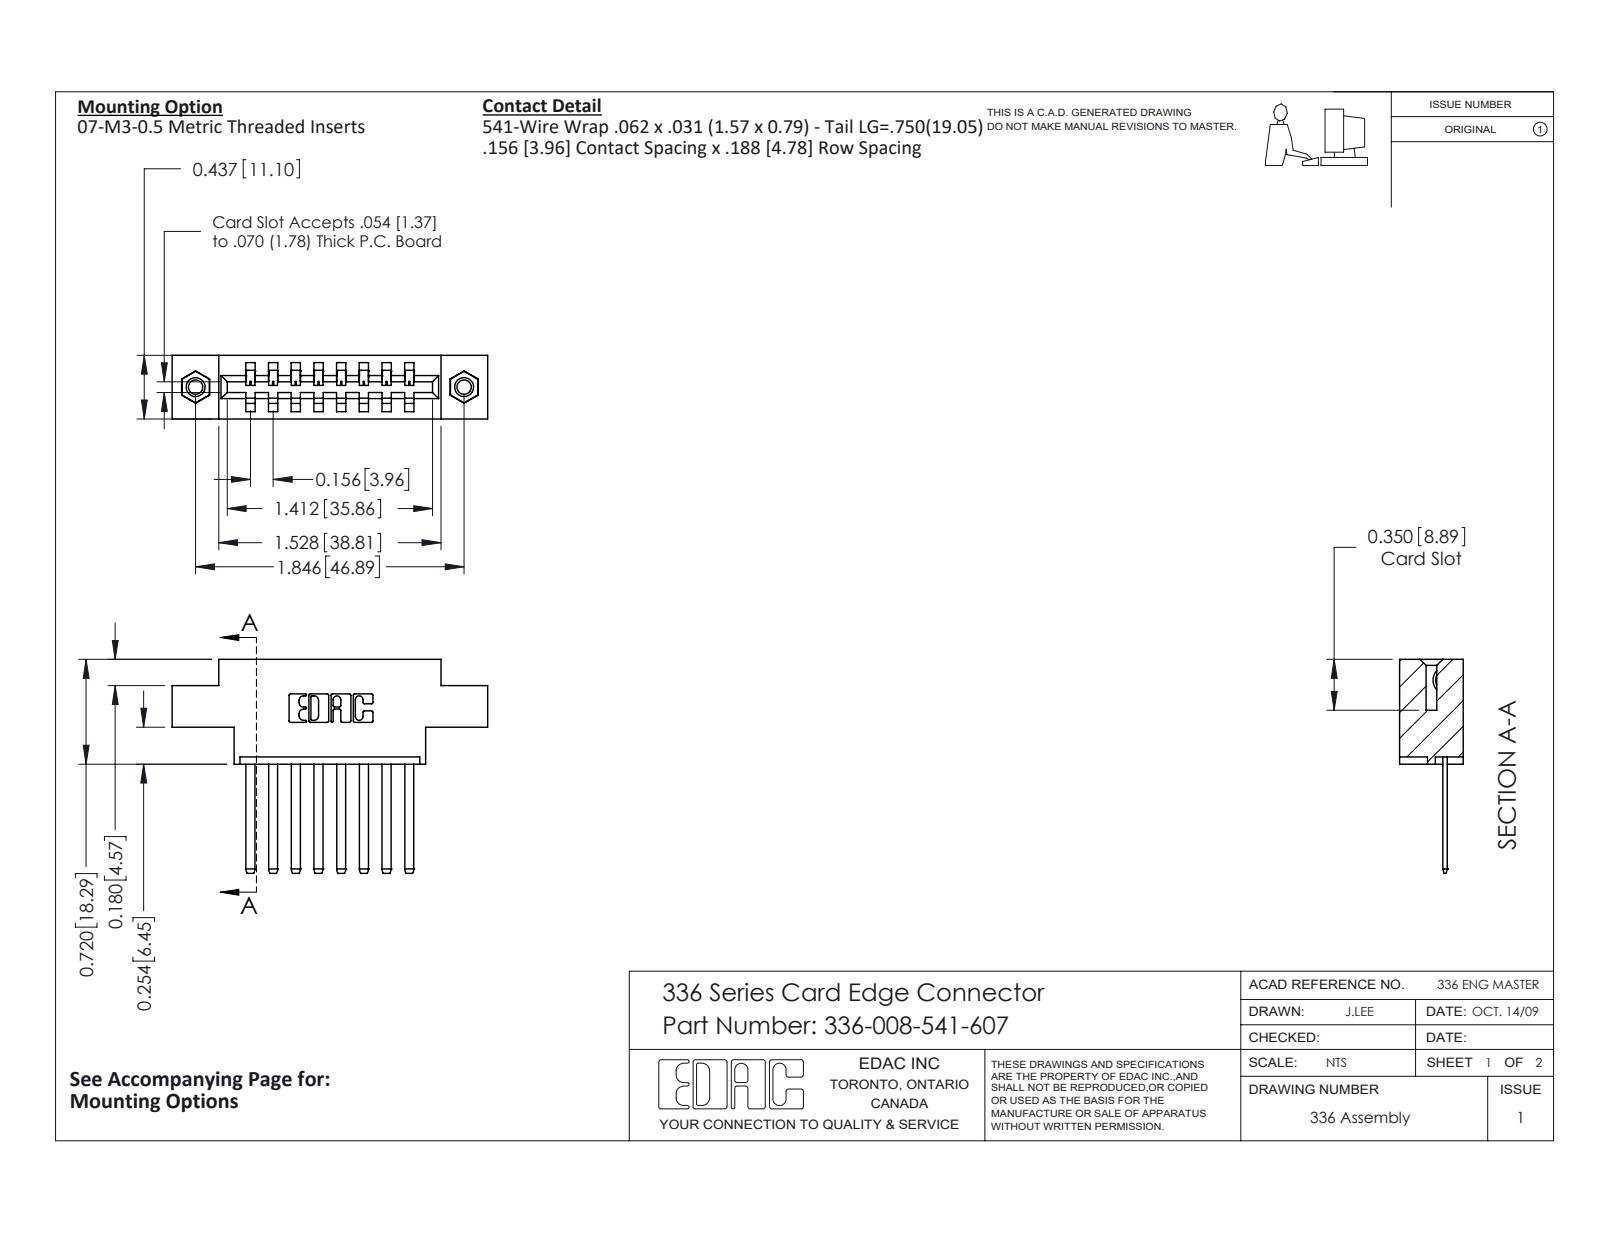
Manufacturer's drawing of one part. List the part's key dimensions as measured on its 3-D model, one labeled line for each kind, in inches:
Part name (STEP PRODUCT): 336-008-541-607; 345-250-001_345-250-005-103; 336-290-001_336-290-541; 336 Part_Offset - .156 Dia - TI
STEP written by: SolidWorks 2020 (CONFIG_CONTROL_DESIGN)
Units: inches
Bodies: 11 solids, 578 faces (378 planar, 184 cylindrical, 16 other)
Overall size (bounding box): 2.169 × 1.47 × 0.437
Volume: 0.429 in³ · Surface area: 11.38 in²
Round holes (diameter × count): ⌀0.098 ×2, ⌀0.125 ×2, ⌀0.156 ×2
Round bosses / shafts (diameter × count): ⌀0.155 ×2
Partial cylindrical surfaces — rounded edges, fillets, slot ends (radius × count): R0.01 ×22, R0.004 ×16, R0.056 ×16, R0.007 ×6, R0.031 ×6, R0.026 ×3, R0.022 ×2, R0.04 ×2
Main face-to-face distances: 0.156, 0.437, 0.468, 0.624, 0.312, 0.312, 0.22, 0.248, 0.181, 0.376
Hole centre spacings: 1.846
